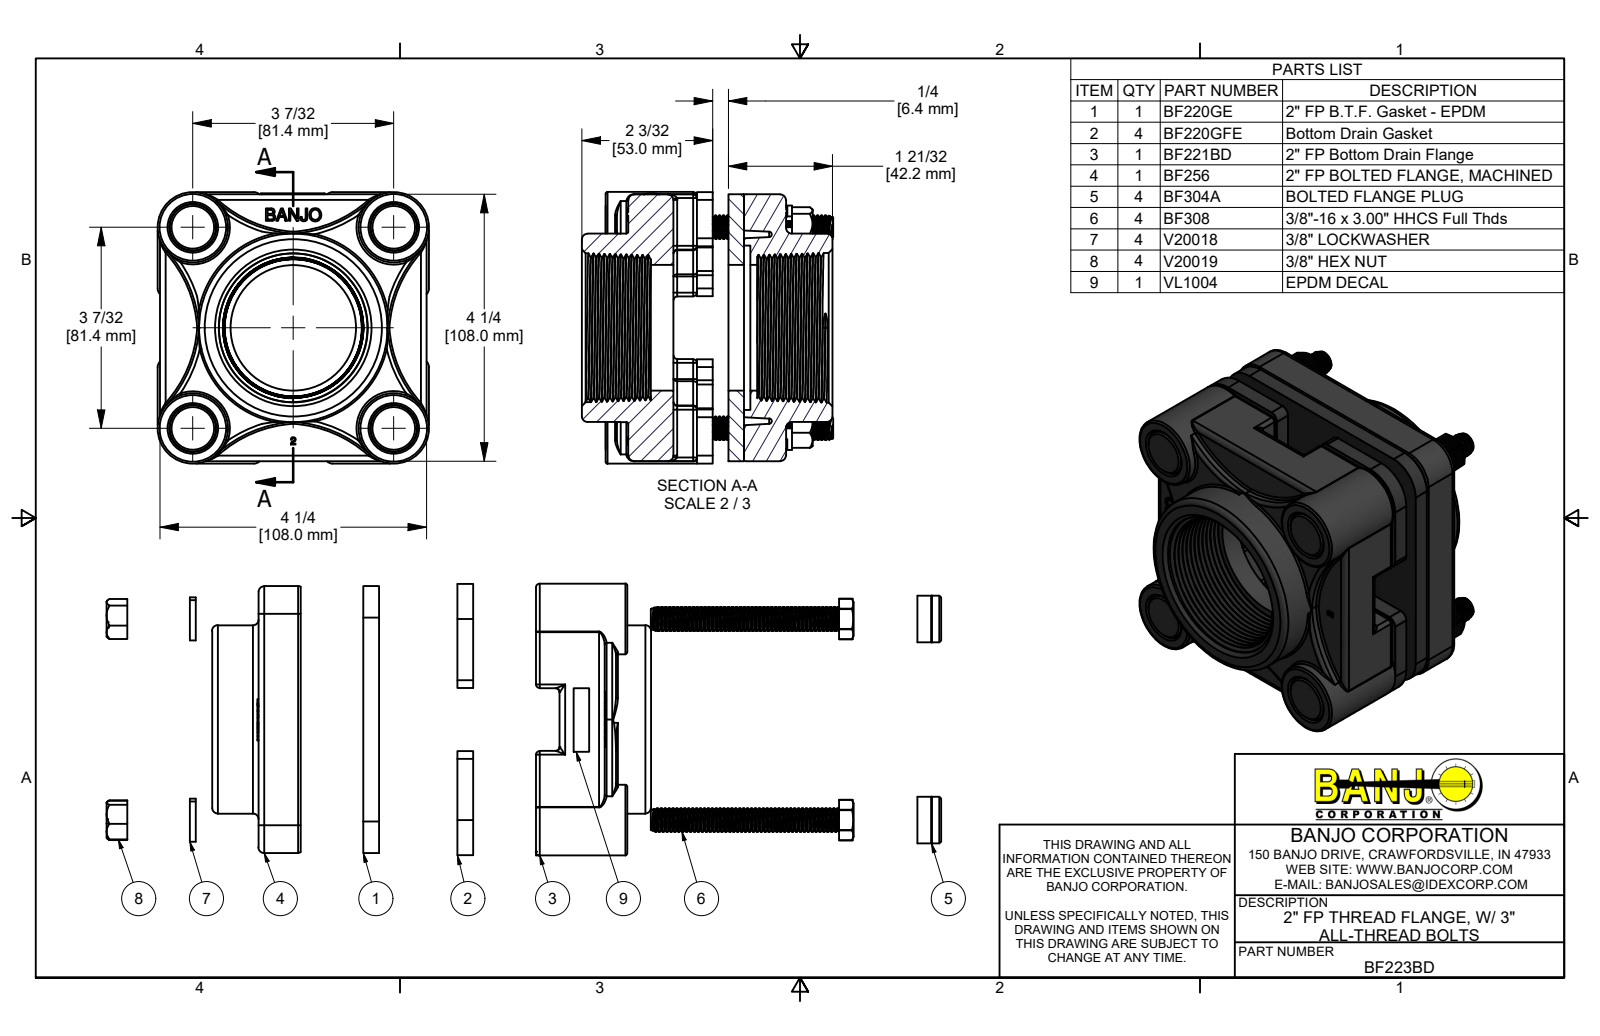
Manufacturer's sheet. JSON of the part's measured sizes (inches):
{"part_name": "BF223BD; BF221BD; BF220GFE; BF220GE (+7 more)", "step_written_by": "Autodesk Inventor 2019 (AUTOMOTIVE_DESIGN)", "units": "inches", "bodies": {"solids": 24, "faces": 1928, "planar": 414, "cylindrical": 689, "other": 825}, "overall_size": [38.212, 4.328, 4.328], "volume_in3": 34.72, "surface_area_in2": 529.6, "round_holes": [[0.307, 4], [0.375, 4], [0.38, 4], [0.385, 4], [0.41, 4], [0.438, 4], [0.72, 4], [0.745, 4], [2, 1], [2.62, 1], [3, 1]], "round_bosses_or_shafts": [[0.324, 188], [1.125, 4], [0.742, 4], [0.687, 4], [0.375, 4]], "partial_cylinders_radius": [[0.06, 44], [0.125, 24], [0.09, 16], [0.03, 8], [0.162, 8], [2, 8], [0.322, 4], [0.44, 4]], "face_to_face_distances": [0.25, 0.25, 4.25, 0.67, 0.92, 1.17, 0.5, 1.42, 0.75, 0.5], "hole_center_spacings": [3.204, 2.265, 2.265, 3.203, 3.204, 4.53, 4.53, 4.531]}
